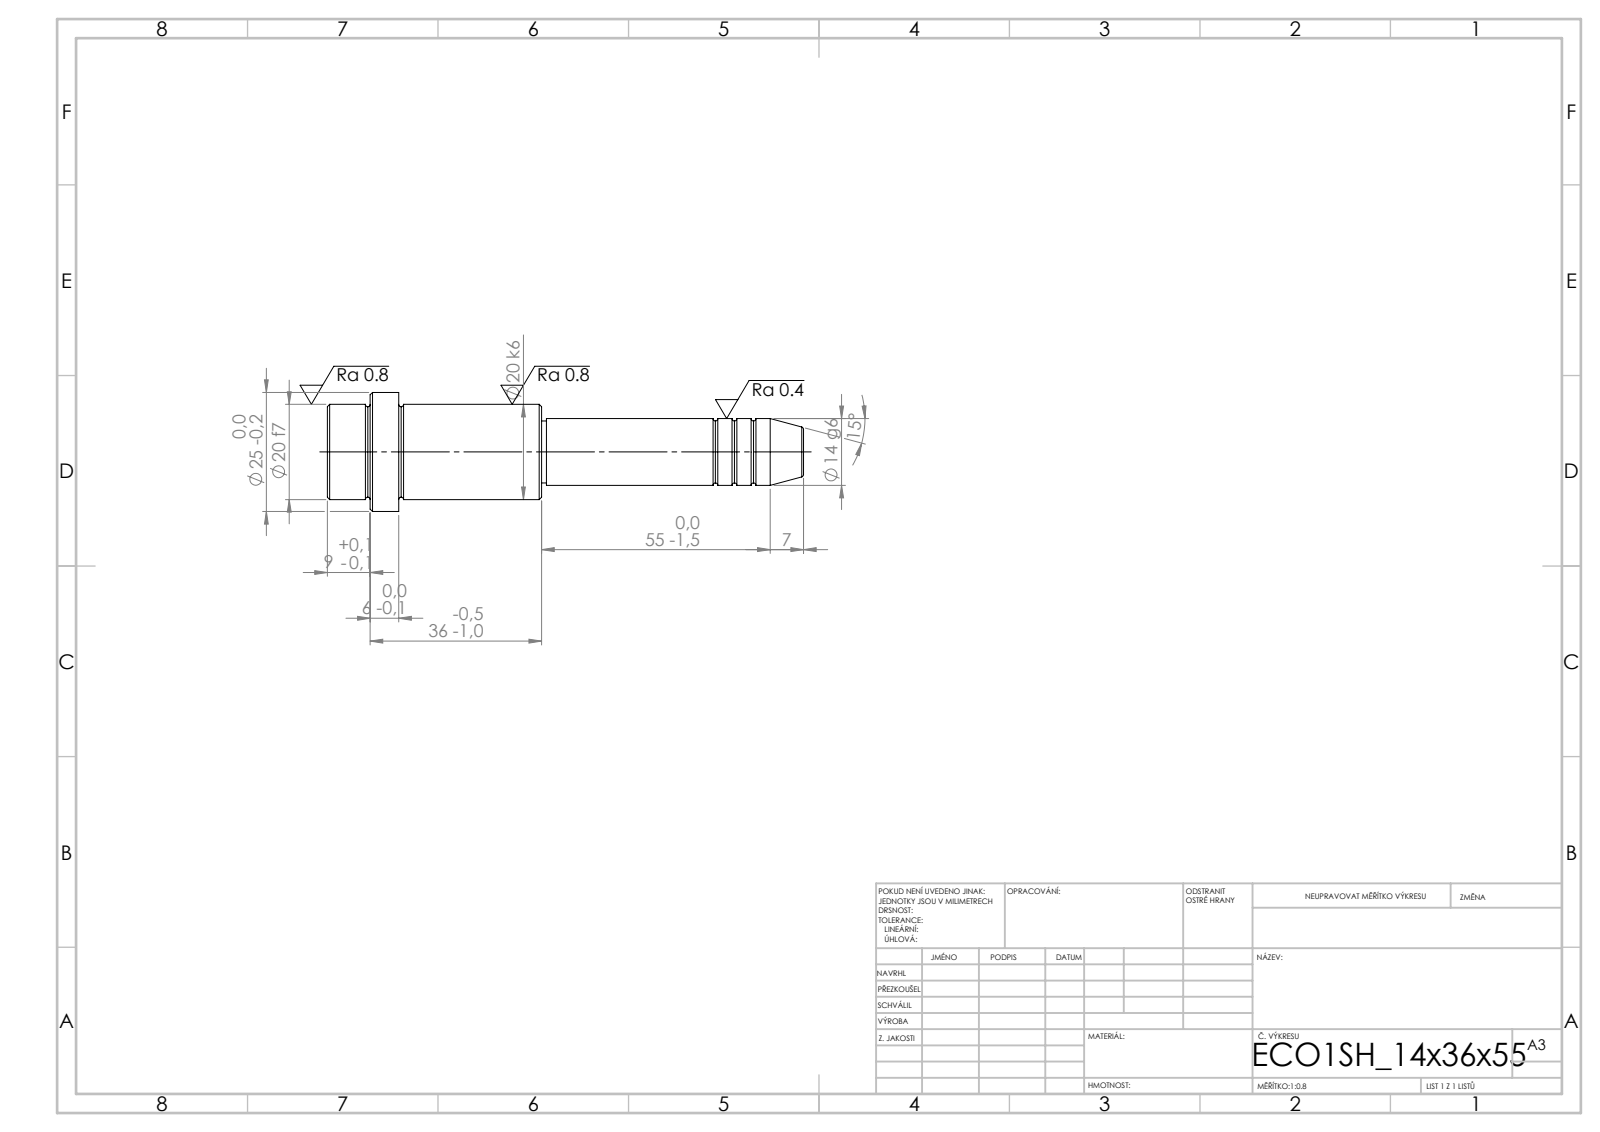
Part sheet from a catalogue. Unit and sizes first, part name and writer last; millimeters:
Units: millimetres
Overall size (bounding box): 100 × 25 × 25
Round bosses / shafts (diameter × count): ⌀25 ×1, ⌀20 ×1, ⌀14 ×1, ⌀13 ×1
Main face-to-face distances: 15, 30, 45, 36, 6, 9, 55, 85, 91, 100
Volume: 23 255 mm³ · Surface area: 6 325 mm²
Bodies: 1 solid, 52 faces (6 planar, 16 cylindrical, 30 other)
STEP written by: SolidWorks 2019 (CONFIG_CONTROL_DESIGN)
